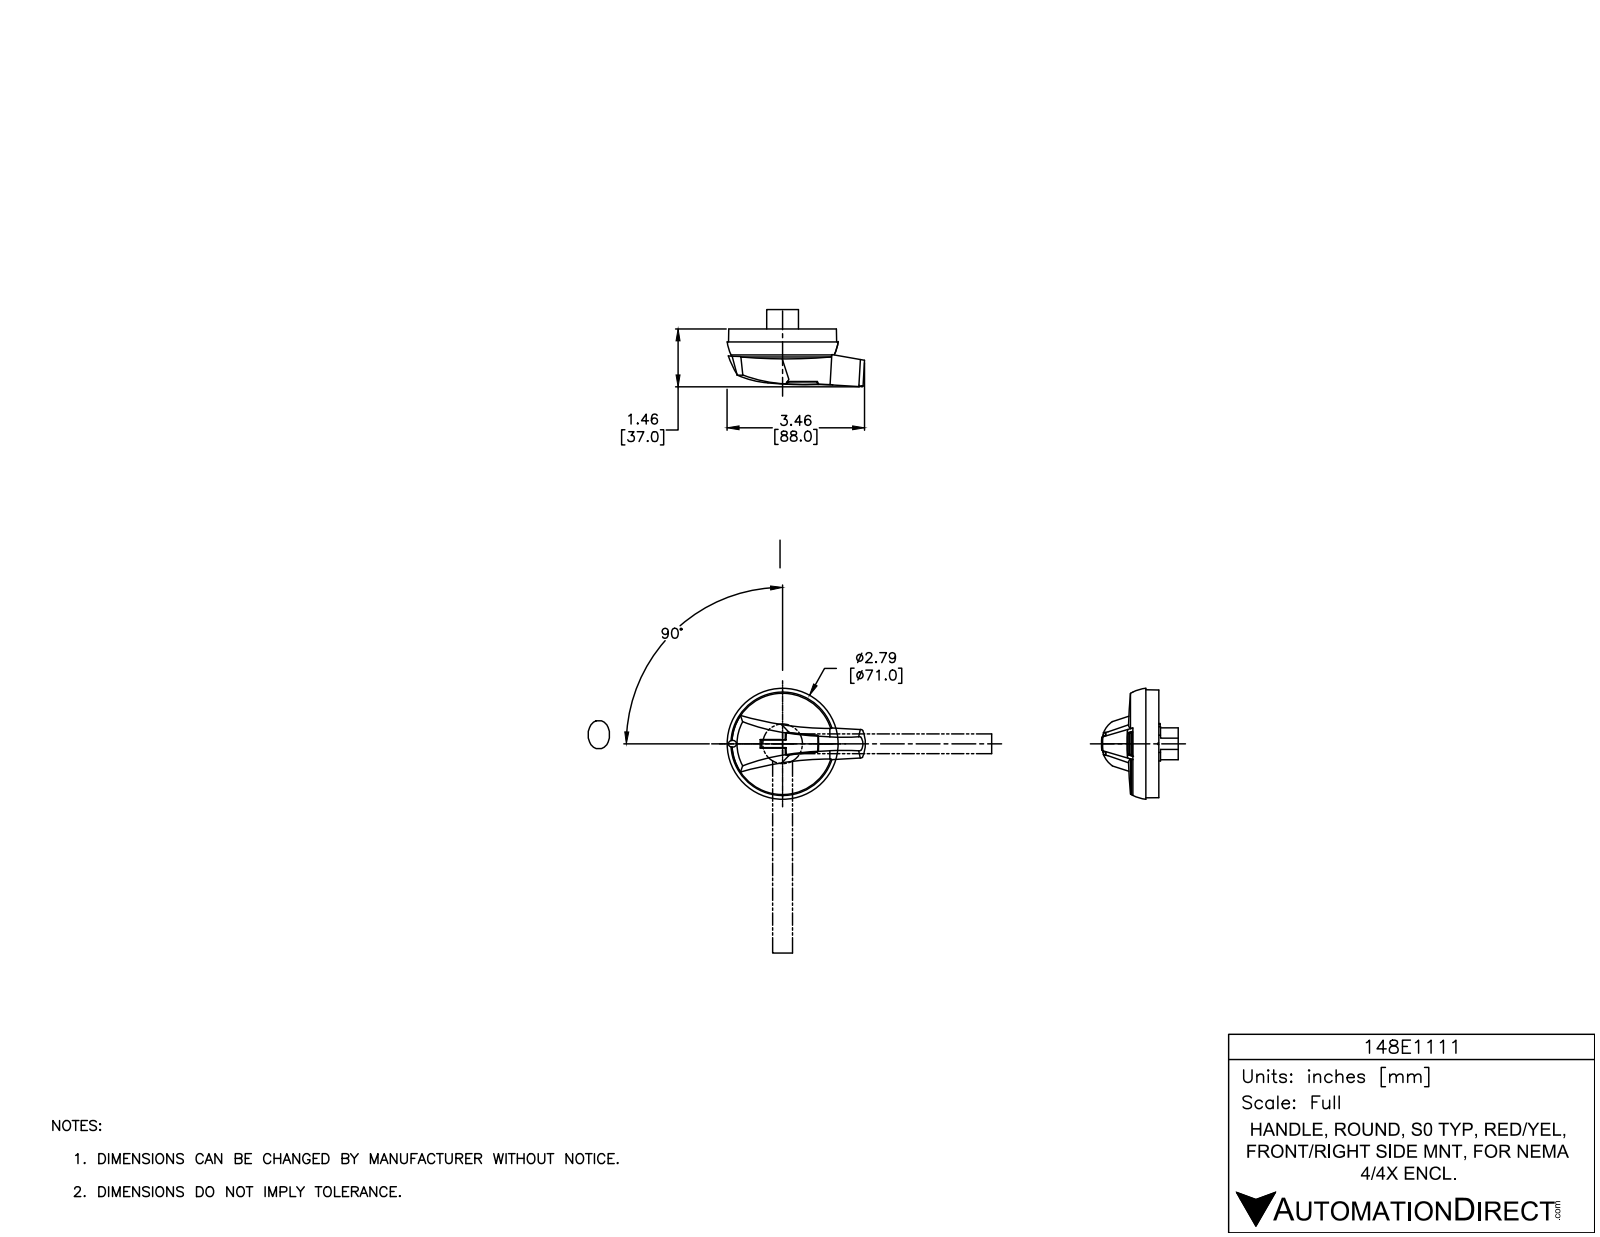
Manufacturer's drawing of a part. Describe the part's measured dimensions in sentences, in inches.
The part is named "148E1111". Its 3-D file was written by "SolidWorks 2015 (AUTOMOTIVE_DESIGN)". It is 5 solids with 1981 faces: 411 planar, 317 cylindrical and 1253 other. Overall it measures 3.479 by 2.8 by 1.925 inches. Its volume is 3.26 cubic inches and its surface area 89.11 square inches. Round holes: 4 of diameter 0.169, 4 of diameter 0.193, 4 of diameter 0.394, 3 of diameter 0.079, 2 of diameter 0.13, 2 of diameter 0.157, 2 of diameter 0.335, 1 of diameter 0.118, 1 of diameter 0.126, 1 of diameter 0.457, 1 of diameter 2.618. Round bosses or shafts: 1 of diameter 2.559. Partial cylindrical surfaces (rounded edges, fillets, slot ends): 96 of radius 0.02, 19 of radius 0.01, 11 of radius 0.039, 10 of radius 0.012, 8 of radius 0.03, 4 of radius 0.142, 4 of radius 0.187, 1 of radius 0.015. The main face-to-face distances are 0.059, 0.071, 0.13, 0.616, 0.053, 0.03, 0.557, 0.486, 0.152, 0.295. The hole center spacings are 0.564, 0.961, 1.557, 1.181, 0.669, 0.677, 0.844, 1.102.
